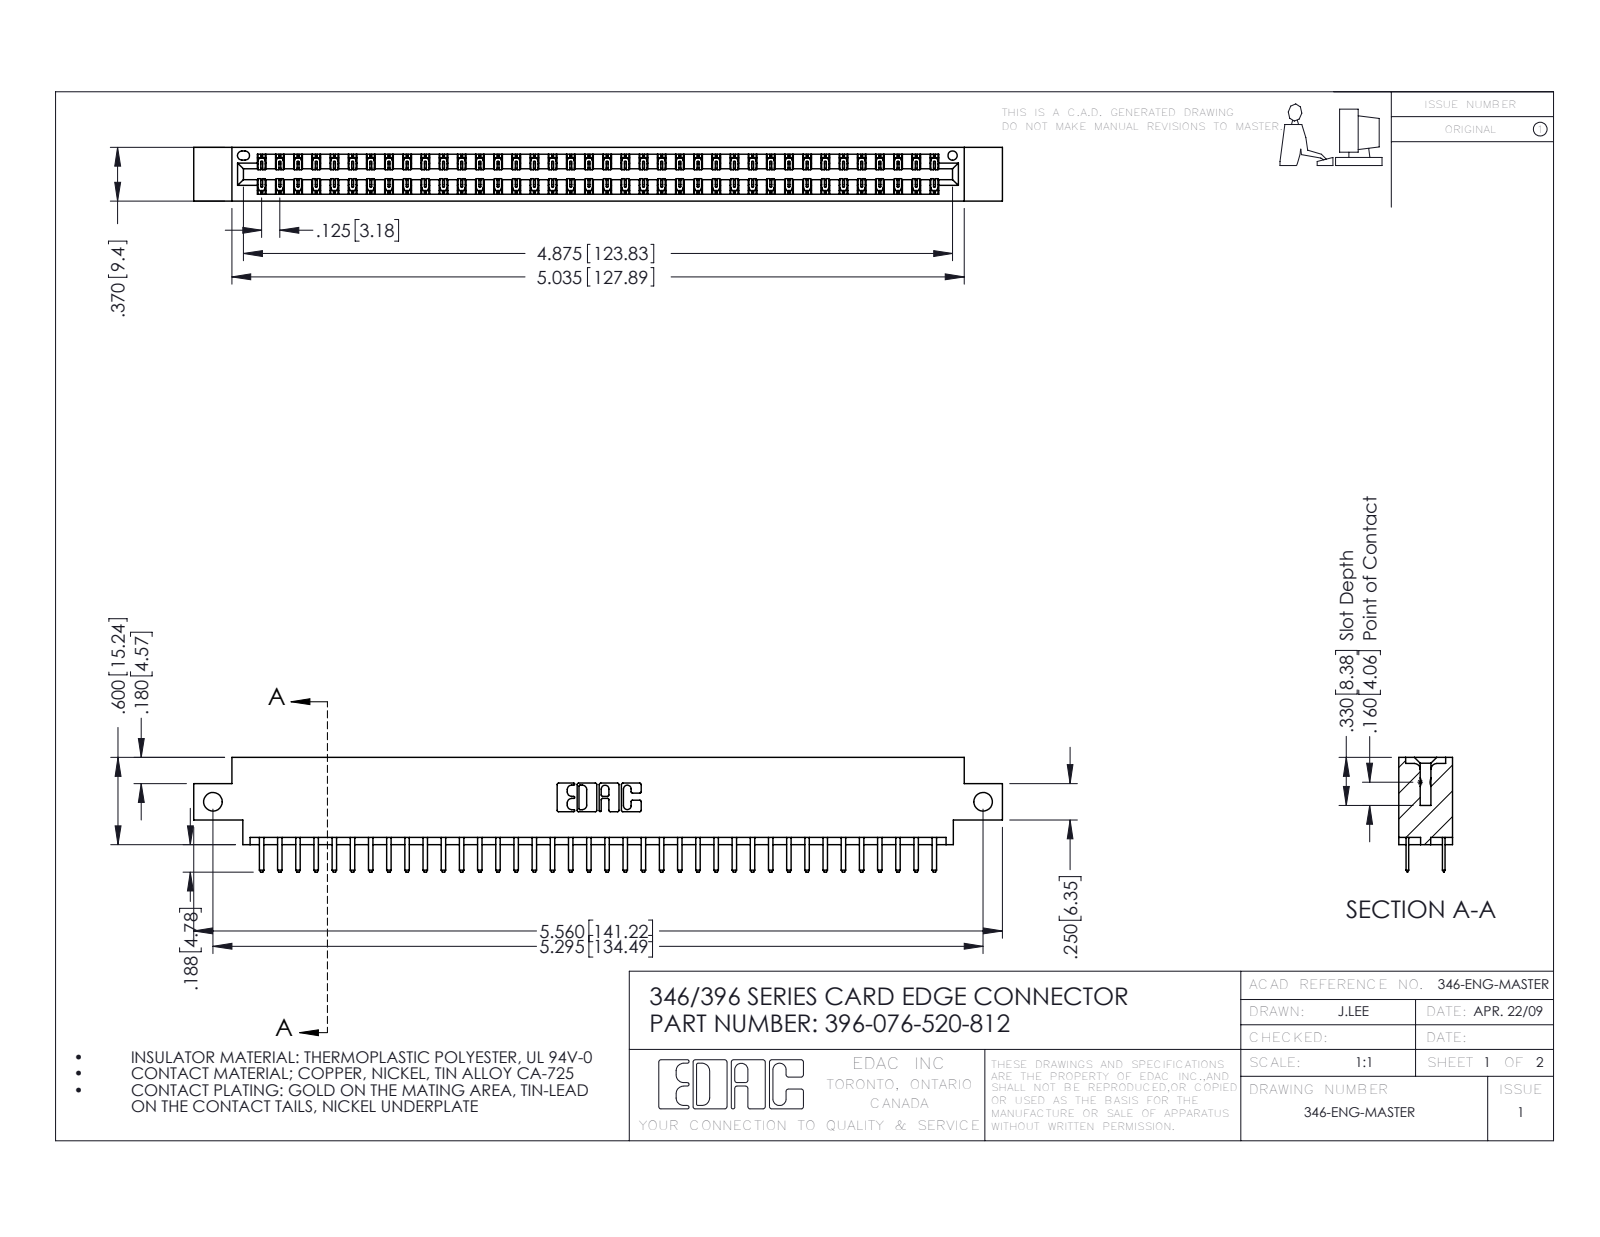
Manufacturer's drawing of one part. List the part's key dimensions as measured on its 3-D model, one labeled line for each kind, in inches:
Part name (STEP PRODUCT): 345-292-001_345-293-120; 396-076-520-812; 346 Part_0.170 Offset - Side Mount
STEP written by: SolidWorks 2016 (CONFIG_CONTROL_DESIGN)
Units: inches
Bodies: 77 solids, 4382 faces (2892 planar, 1490 cylindrical, 0 other)
Overall size (bounding box): 5.56 × 0.788 × 0.37
Volume: 0.822 in³ · Surface area: 28.53 in²
Round holes (diameter × count): ⌀0.128 ×2, ⌀0.064 ×1
Partial cylindrical surfaces — rounded edges, fillets, slot ends (radius × count): R0.006 ×114, R0.01 ×80, R0.01 ×22, R0.007 ×6, R0.031 ×6, R0.026 ×3, R0.014 ×2, R0.022 ×2
Main face-to-face distances: 0.048, 0.322, 0.25, 0.37, 0.275, 0.072, 0.298, 0.025, 0.148, 0.222
Hole centre spacings: 5.295
